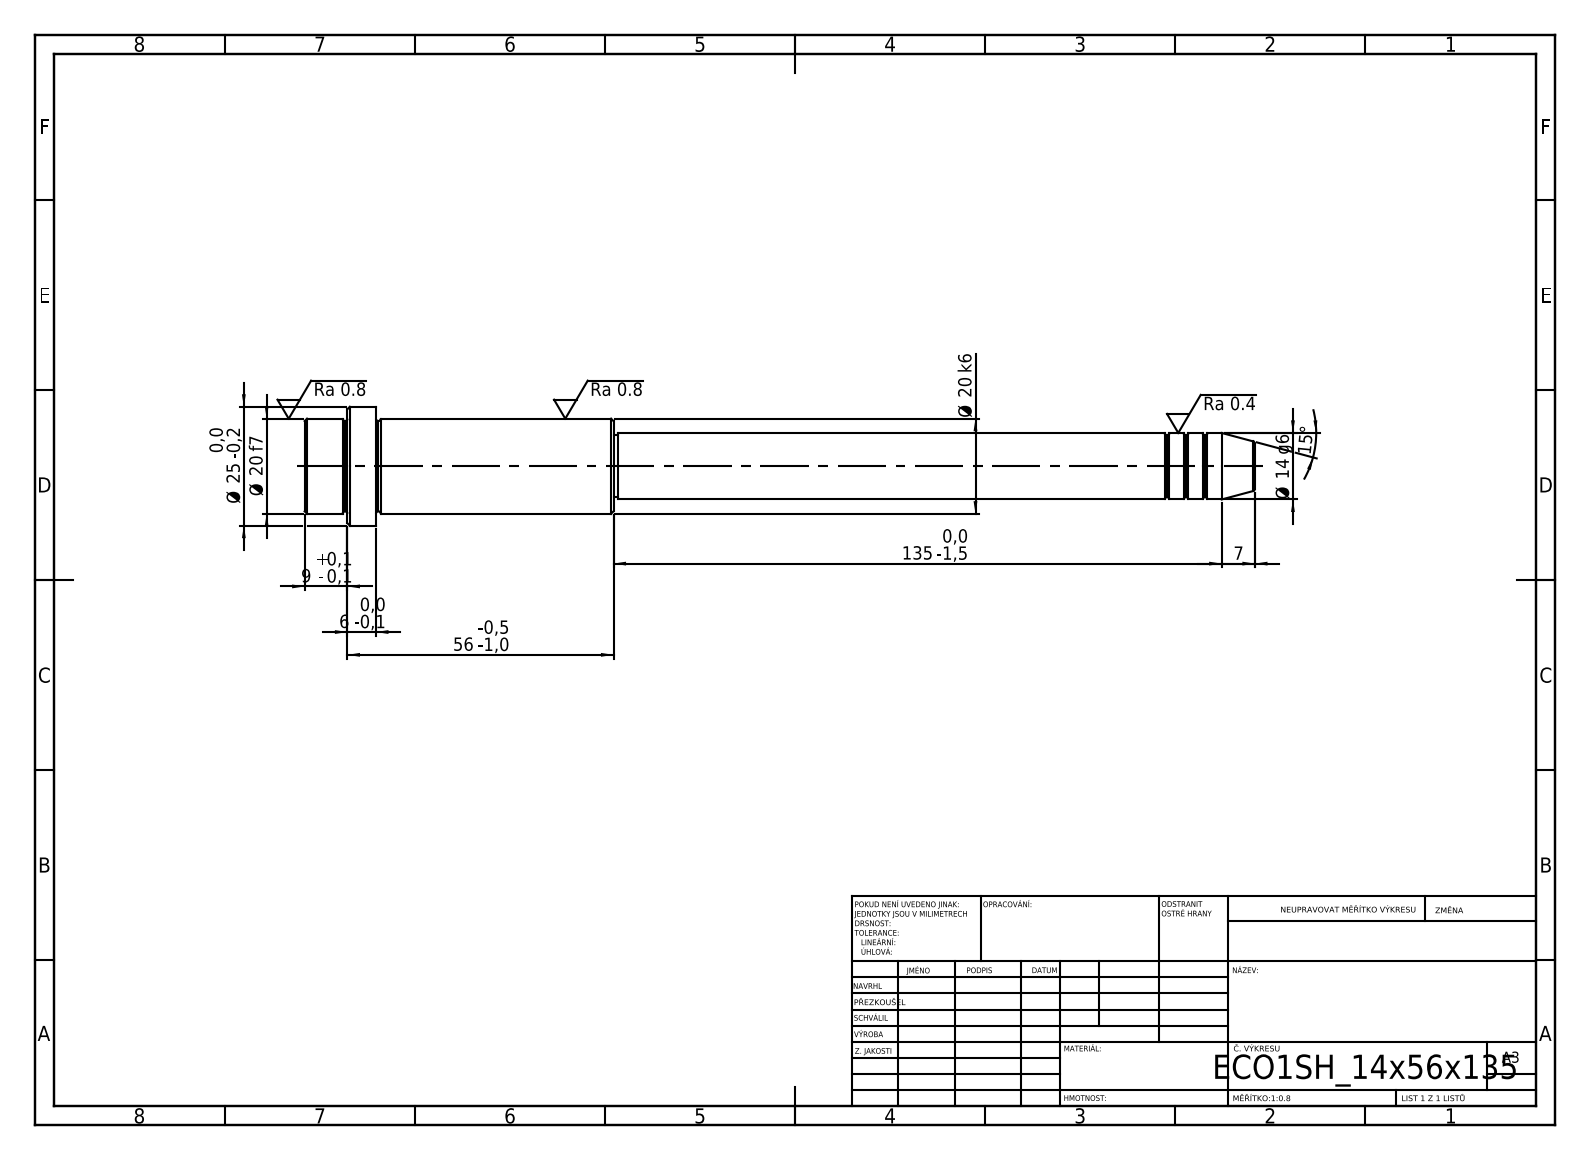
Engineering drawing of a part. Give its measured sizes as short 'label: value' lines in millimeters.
written by: SolidWorks 2019 (CONFIG_CONTROL_DESIGN)
unit: mm
bodies: 1 solid, 52 faces (6 planar, 16 cylindrical, 30 other)
size: 200 × 25 × 25
volume: 41 854 mm³; area: 11 101 mm²
bosses: 1× ⌀25, 1× ⌀20, 1× ⌀14, 1× ⌀13
face distances: 15, 50, 65, 56, 6, 9, 135, 185, 191, 200
